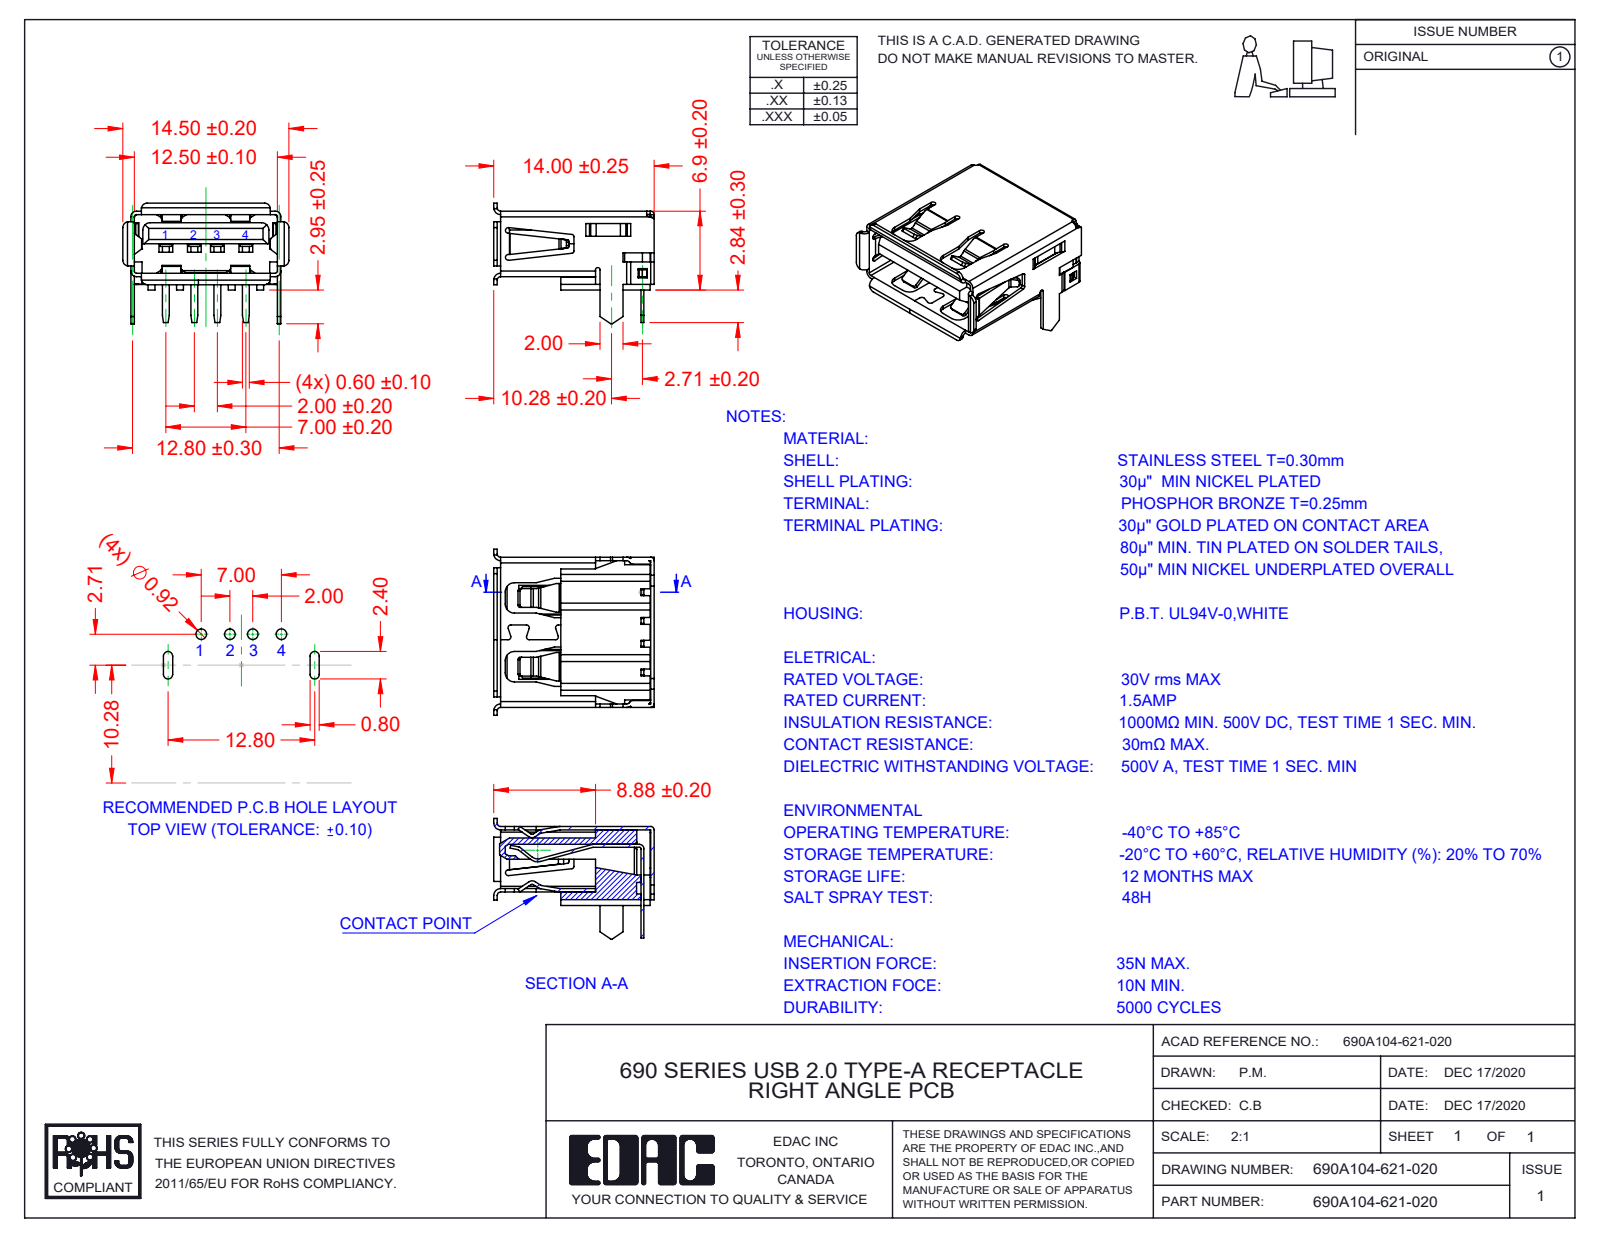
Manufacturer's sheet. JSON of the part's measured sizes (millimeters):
{"part_name": "Insulator 690A104-621-020; Shell 690A104-621-020; 690A104-621-020; Contact 690A104-621-020", "step_written_by": "SolidWorks 2020 (AUTOMOTIVE_DESIGN)", "units": "millimeters", "bodies": {"solids": 6, "faces": 815, "planar": 630, "cylindrical": 171, "other": 14}, "overall_size": [14.5, 14, 10.54], "volume_mm3": 575, "surface_area_mm2": 2120, "partial_cylinders_radius": [[0.2, 31], [0.5, 24], [0.3, 16], [0.25, 10], [0.1, 8], [0.6, 8], [0.8, 8], [0.24, 4]], "face_to_face_distances": [5.42, 5.12, 12.8, 1.01, 1.56, 1.26, 0.55, 0.71, 1.2, 4.16]}
